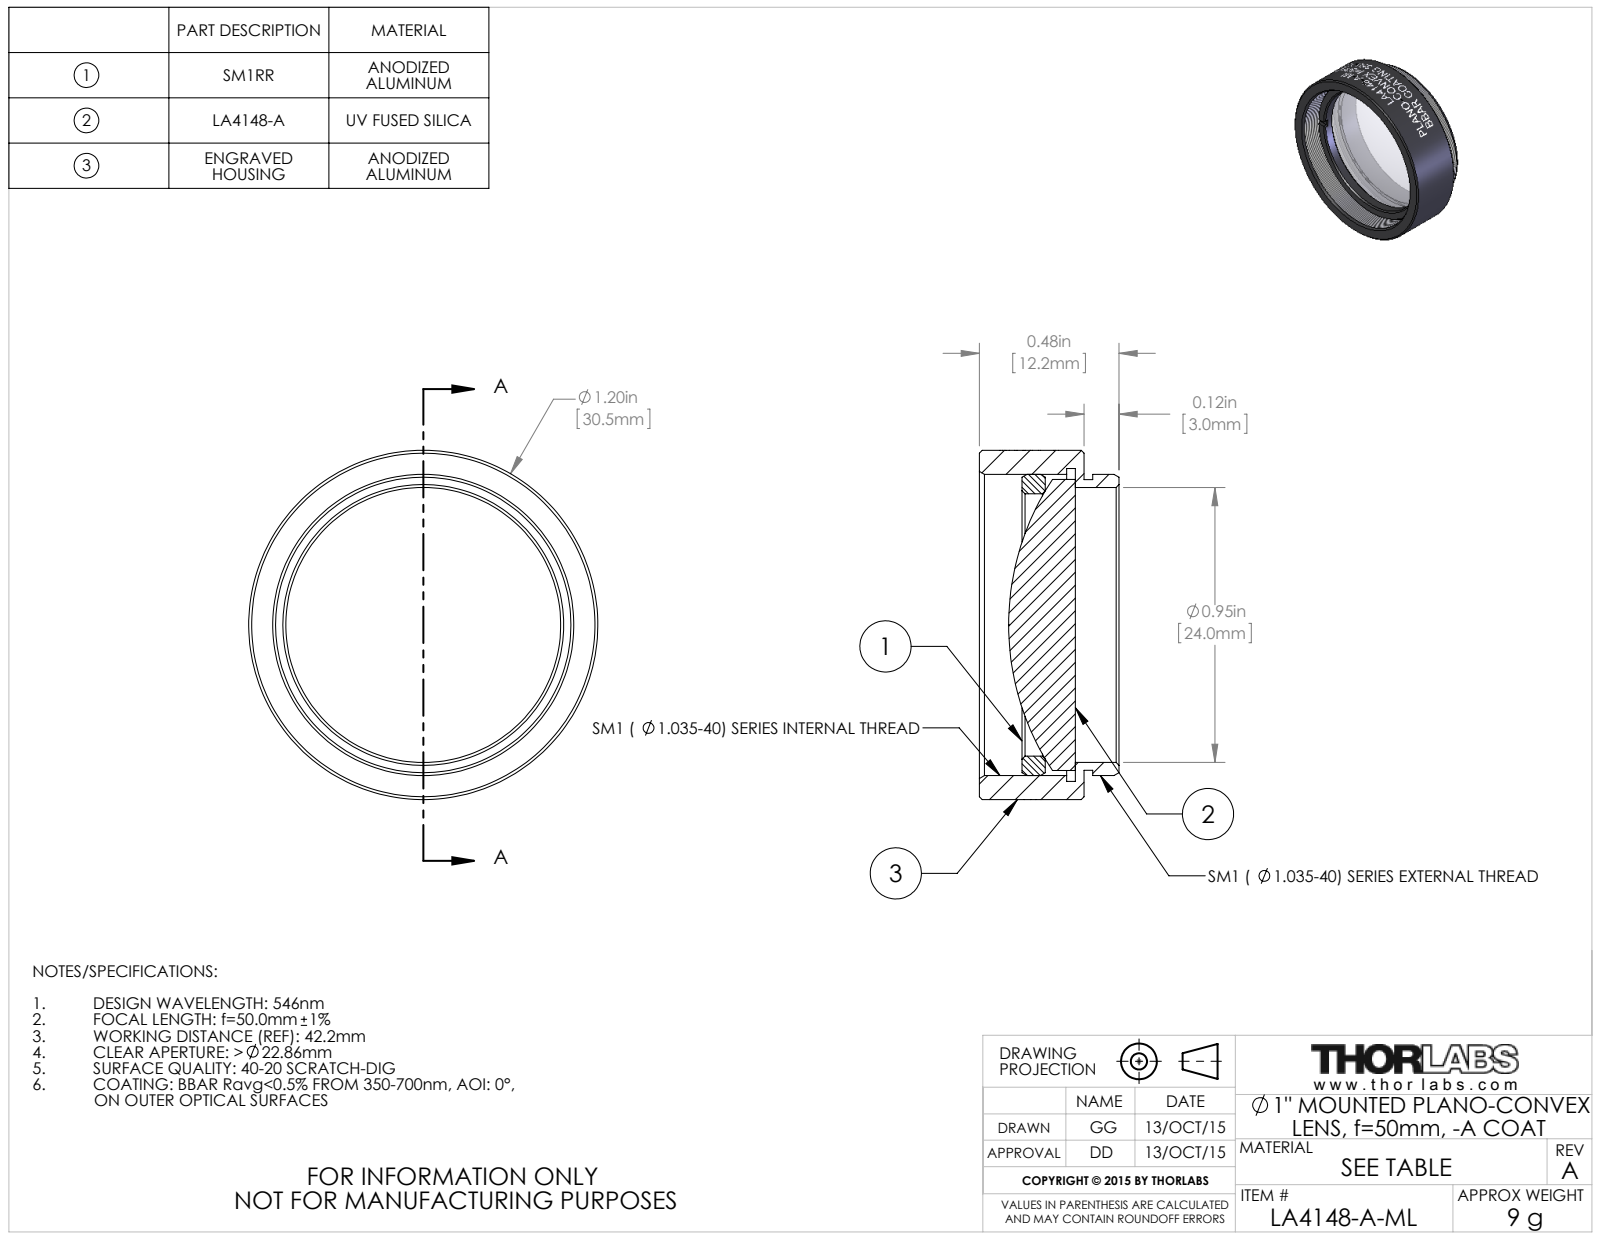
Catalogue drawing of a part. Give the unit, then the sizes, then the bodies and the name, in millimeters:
Units: millimetres
Overall size (bounding box): 30.48 × 30.48 × 12.19
Round holes (diameter × count): ⌀22.91 ×1, ⌀24 ×1, ⌀26.29 ×1, ⌀27.3 ×1
Round bosses / shafts (diameter × count): ⌀30.48 ×1, ⌀26.29 ×1, ⌀25.4 ×1, ⌀25.37 ×1
Main face-to-face distances: 0.76, 8.38, 9.14, 5.76, 2.62, 3.38, 3.73, 2.03, 4.65, 5.41
Volume: 4 234 mm³ · Surface area: 4 494 mm²
Bodies: 3 solids, 156 faces (20 planar, 112 cylindrical, 24 other)
Part name (STEP PRODUCT): TTN039165-E0W
STEP written by: SolidWorks 2014 (CONFIG_CONTROL_DESIGN)
